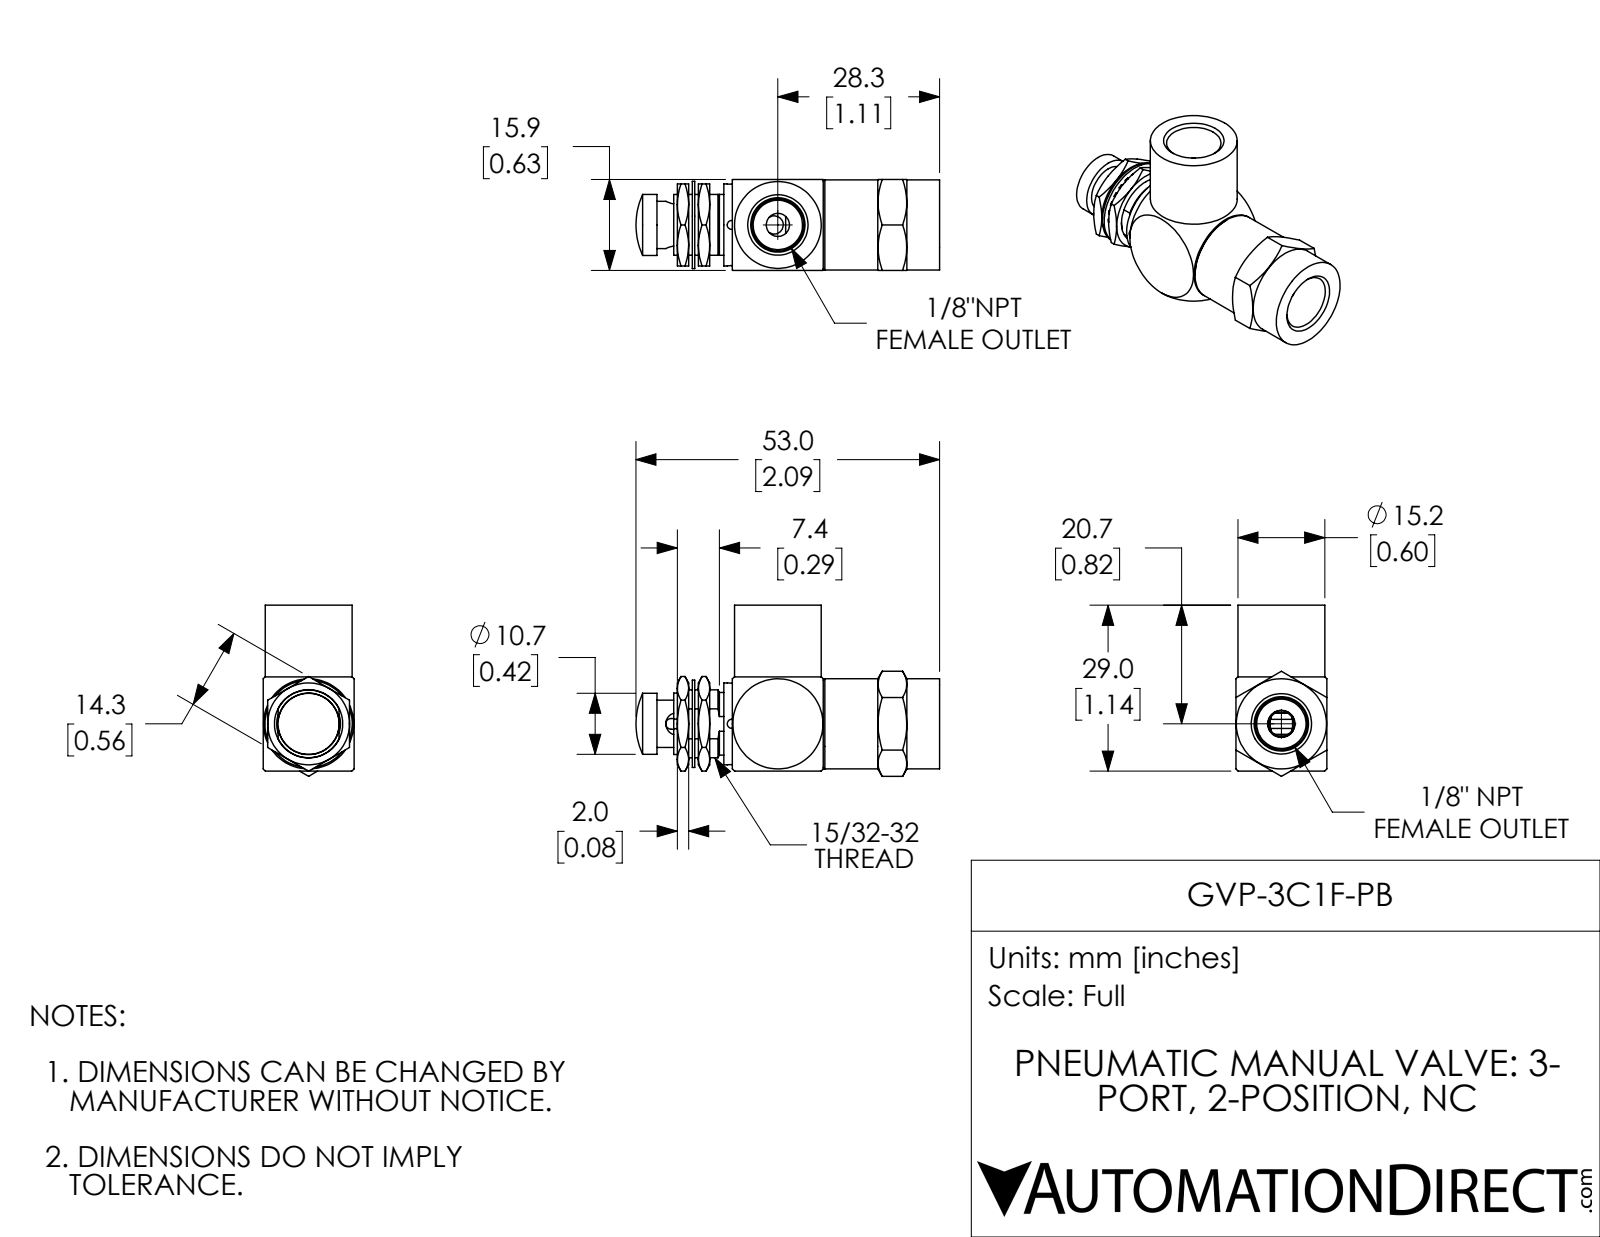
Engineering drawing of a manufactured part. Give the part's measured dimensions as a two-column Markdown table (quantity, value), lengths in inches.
| quantity | value |
| --- | --- |
| part name | GVP-3C1F-PB |
| STEP written by | SolidWorks 2018 (AUTOMOTIVE_DESIGN) |
| units | inches |
| bodies | 8 solids, 343 faces (124 planar, 146 cylindrical, 73 other) |
| overall size | 2.088 × 1.176 × 0.625 |
| volume | 0.52 in³ |
| surface area | 13.55 in² |
| round holes (diameter × count) | 0.063 × 3, 0.125 × 2, 0.339 × 2, 0.03 × 1, 0.153 × 1, 0.159 × 1, 0.182 × 1, 0.187 × 1, 0.249 × 1, 0.34 × 1, 0.377 × 1, 0.438 × 1 |
| round bosses / shafts (diameter × count) | 0.62 × 1, 0.6 × 1, 0.597 × 1, 0.563 × 1, 0.495 × 1, 0.445 × 1, 0.43 × 1, 0.423 × 1 |
| partial cylindrical surfaces (radius × count) | 0.037 × 2, 0.233 × 1, 0.239 × 1, 0.26 × 1 |
| main face-to-face distances | 0.625, 0.8, 0.332, 0.072, 0.031, 0.594, 0.145, 0.078, 0.901, 0.158 |
| hole center spacings | 0.291, 0.026, 0.04, 0.317, 0.337, 0.377, 0.629, 0.669 |
